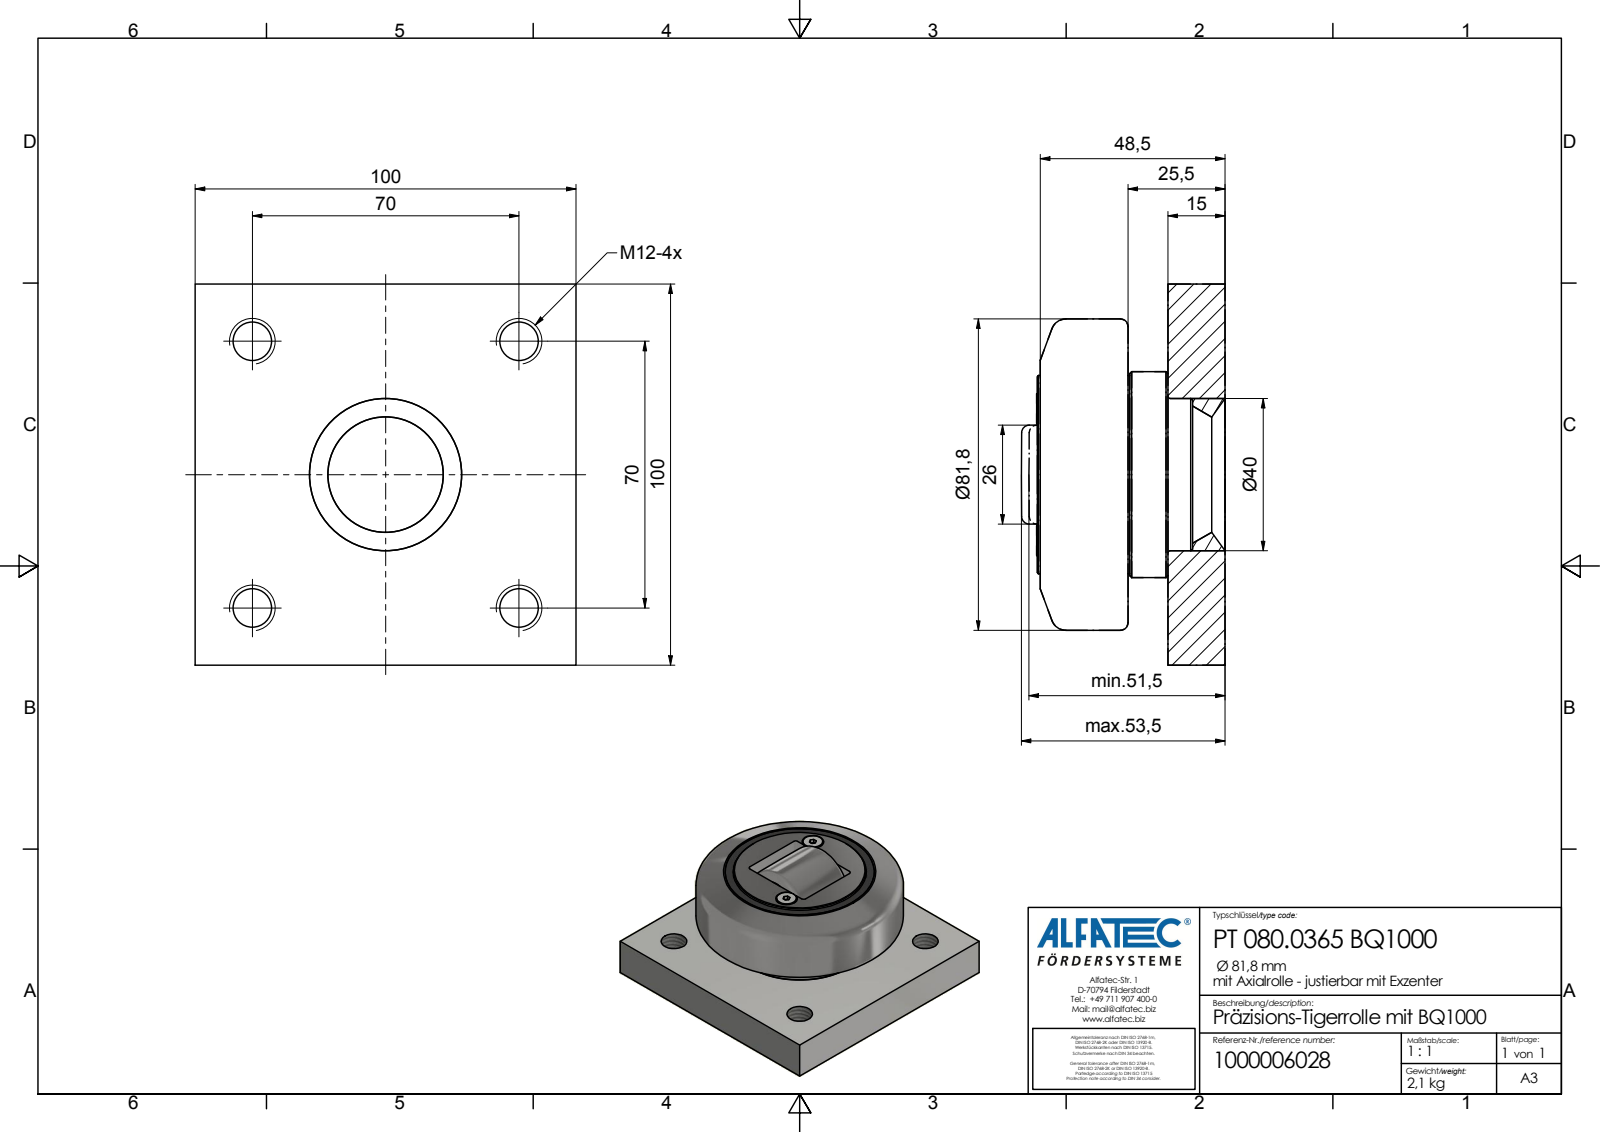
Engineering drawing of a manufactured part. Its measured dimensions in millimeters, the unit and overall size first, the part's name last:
Units: millimetres
Overall size (bounding box): 100 × 100 × 53.5
Round holes (diameter × count): ⌀10.11 ×4
Round bosses / shafts (diameter × count): ⌀7.8 ×2, ⌀54 ×1, ⌀52 ×1
Partial cylindrical surfaces — rounded edges, fillets, slot ends (radius × count): R1 ×4, R11.25 ×1
Main face-to-face distances: 15, 100, 25.5, 10.5, 49.3, 34.3, 23.8, 48.5, 33.5, 23
Hole centre spacings: 70, 98.99
Volume: 283 838 mm³ · Surface area: 40 594 mm²
Bodies: 1 solid, 64 faces (36 planar, 15 cylindrical, 13 other)
Part name (STEP PRODUCT): PT 080.0365 BQ1000_Kontur
STEP written by: Autodesk Inventor 2020 (AP242_MANAGED_MODEL_BASED_3D_ENGINEERING_MIM_LF)
